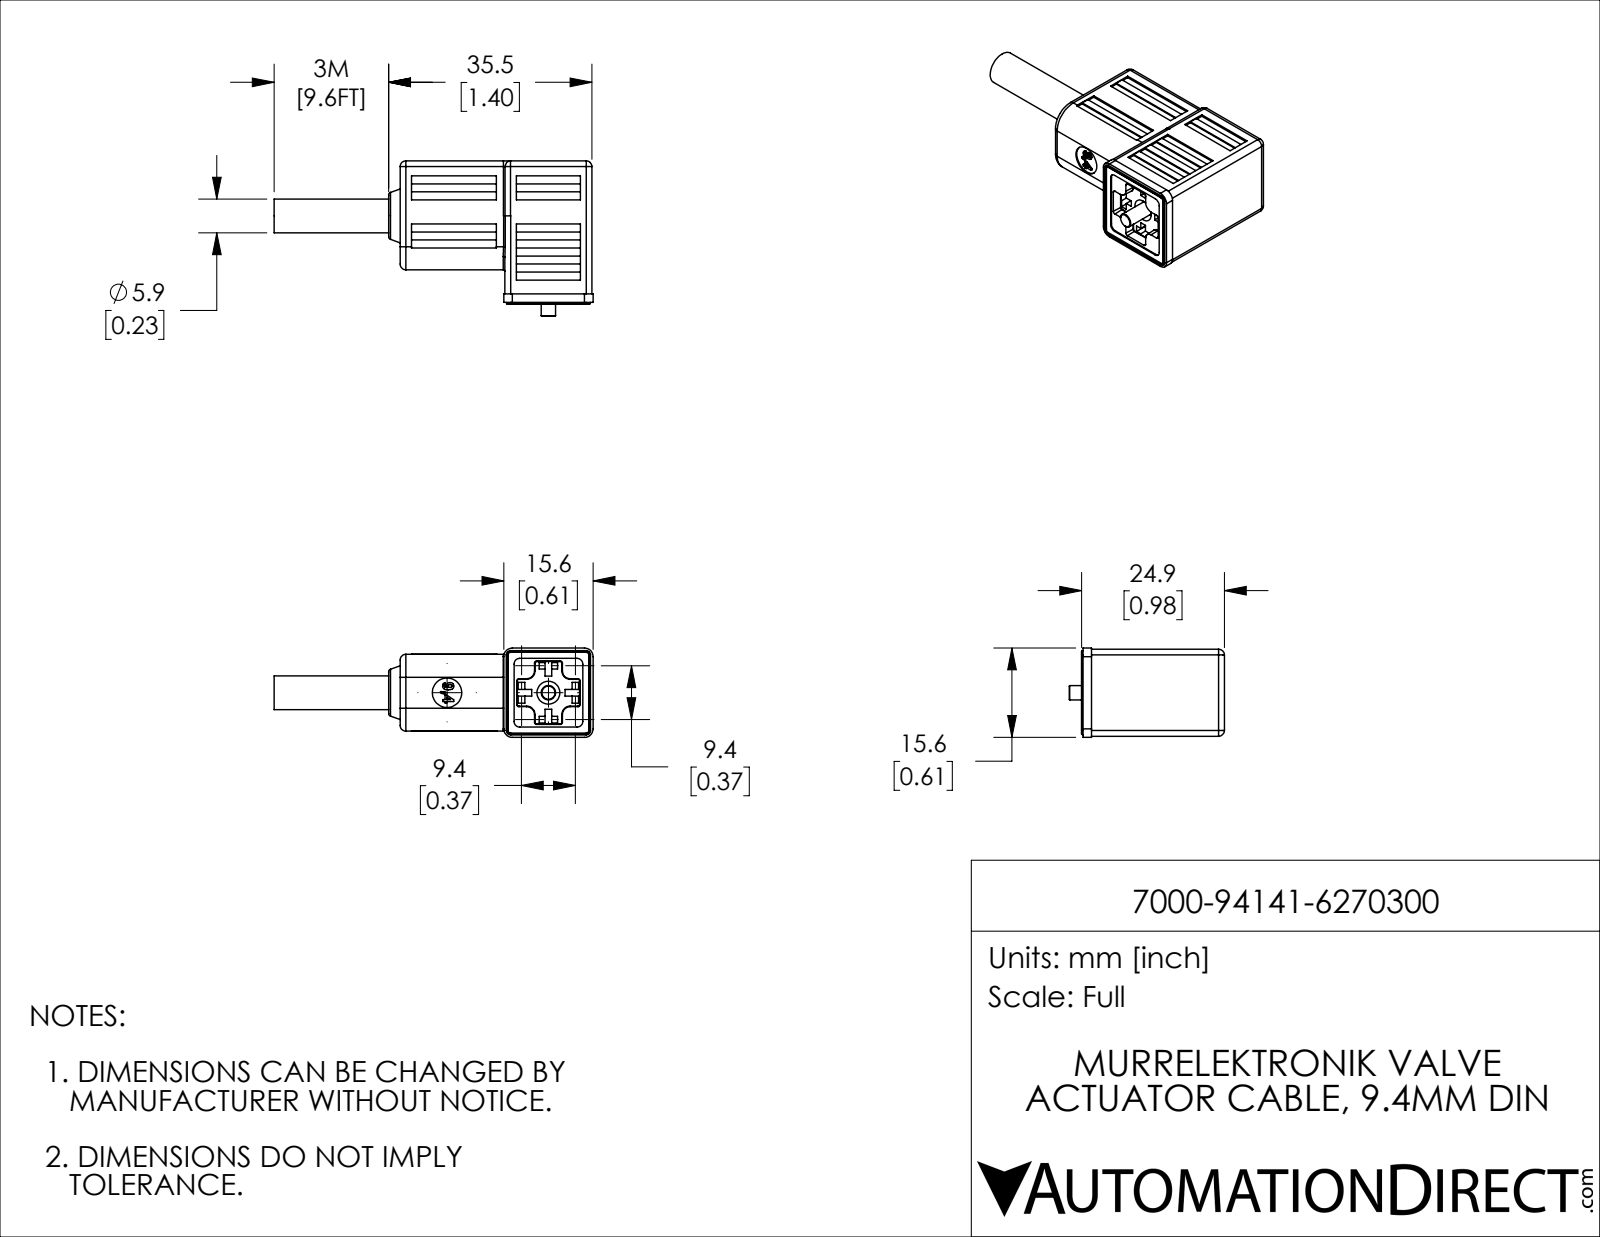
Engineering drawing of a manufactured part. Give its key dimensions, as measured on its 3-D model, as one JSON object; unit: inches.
{"part_name": "7000-94141-6270300", "step_written_by": "SolidWorks 2019 (CONFIG_CONTROL_DESIGN)", "units": "inches", "bodies": {"solids": 1, "faces": 402, "planar": 258, "cylindrical": 60, "other": 84}, "overall_size": [2.193, 1.067, 0.614], "volume_in3": 0.629, "surface_area_in2": 6.728, "round_holes": [[0.157, 1], [0.203, 1], [0.236, 1]], "round_bosses_or_shafts": [[0.232, 1], [0.228, 1], [0.098, 1]], "partial_cylinders_radius": [[0.039, 19], [0.012, 11], [0.057, 4], [0.059, 4], [0.157, 2]], "face_to_face_distances": [0.035, 0.551, 0.563, 0.559, 0.547, 0.047, 0.598, 0.024, 0.587, 0.043], "hole_center_spacings": [0.697]}
